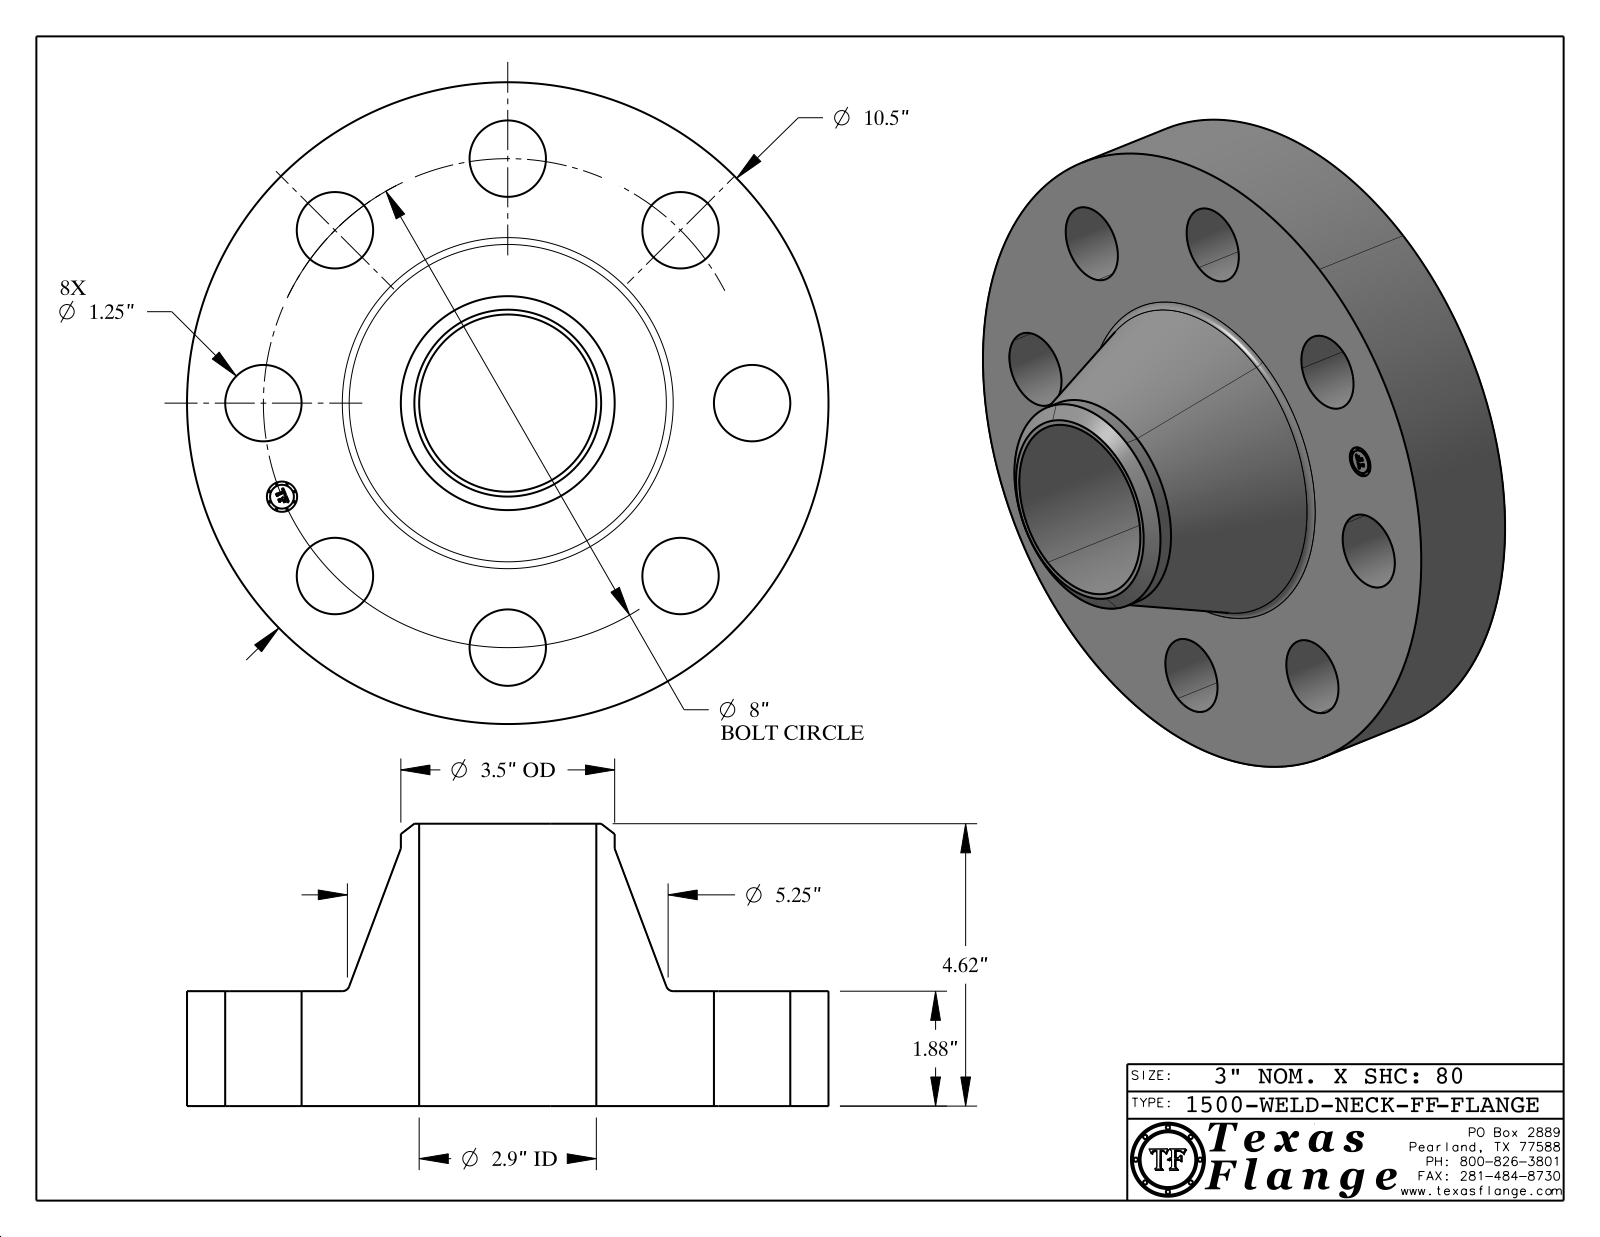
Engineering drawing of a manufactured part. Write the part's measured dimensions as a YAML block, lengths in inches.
part_name: "1500-WELD-NECK-FF"
step_written_by: "CATIA V5 STEP AP214 (AUTOMOTIVE_DESIGN)"
units: inches
bodies: {solids: 1, faces: 416, planar: 368, cylindrical: 42, other: 6}
overall_size: [10.5, 10.5, 4.62]
volume: 153.1
surface_area: 328.7
round_holes:
  - {diameter: 1.25, count: 8}
  - {diameter: 0.495, count: 1}
  - {diameter: 2.9, count: 1}
round_bosses_or_shafts:
  - {diameter: 0.03, count: 8}
  - {diameter: 10.5, count: 1}
  - {diameter: 3.5, count: 1}
  - {diameter: 0.39, count: 1}
face_to_face_distances: [1.88, 4.62, 2.74, 0.015, 1.865, 2.755, 0.148, 0.145, 0.027, 0.096]
hole_center_spacings: [4, 3.061, 5.657, 7.391, 1.561, 6.652, 7.846, 8]
